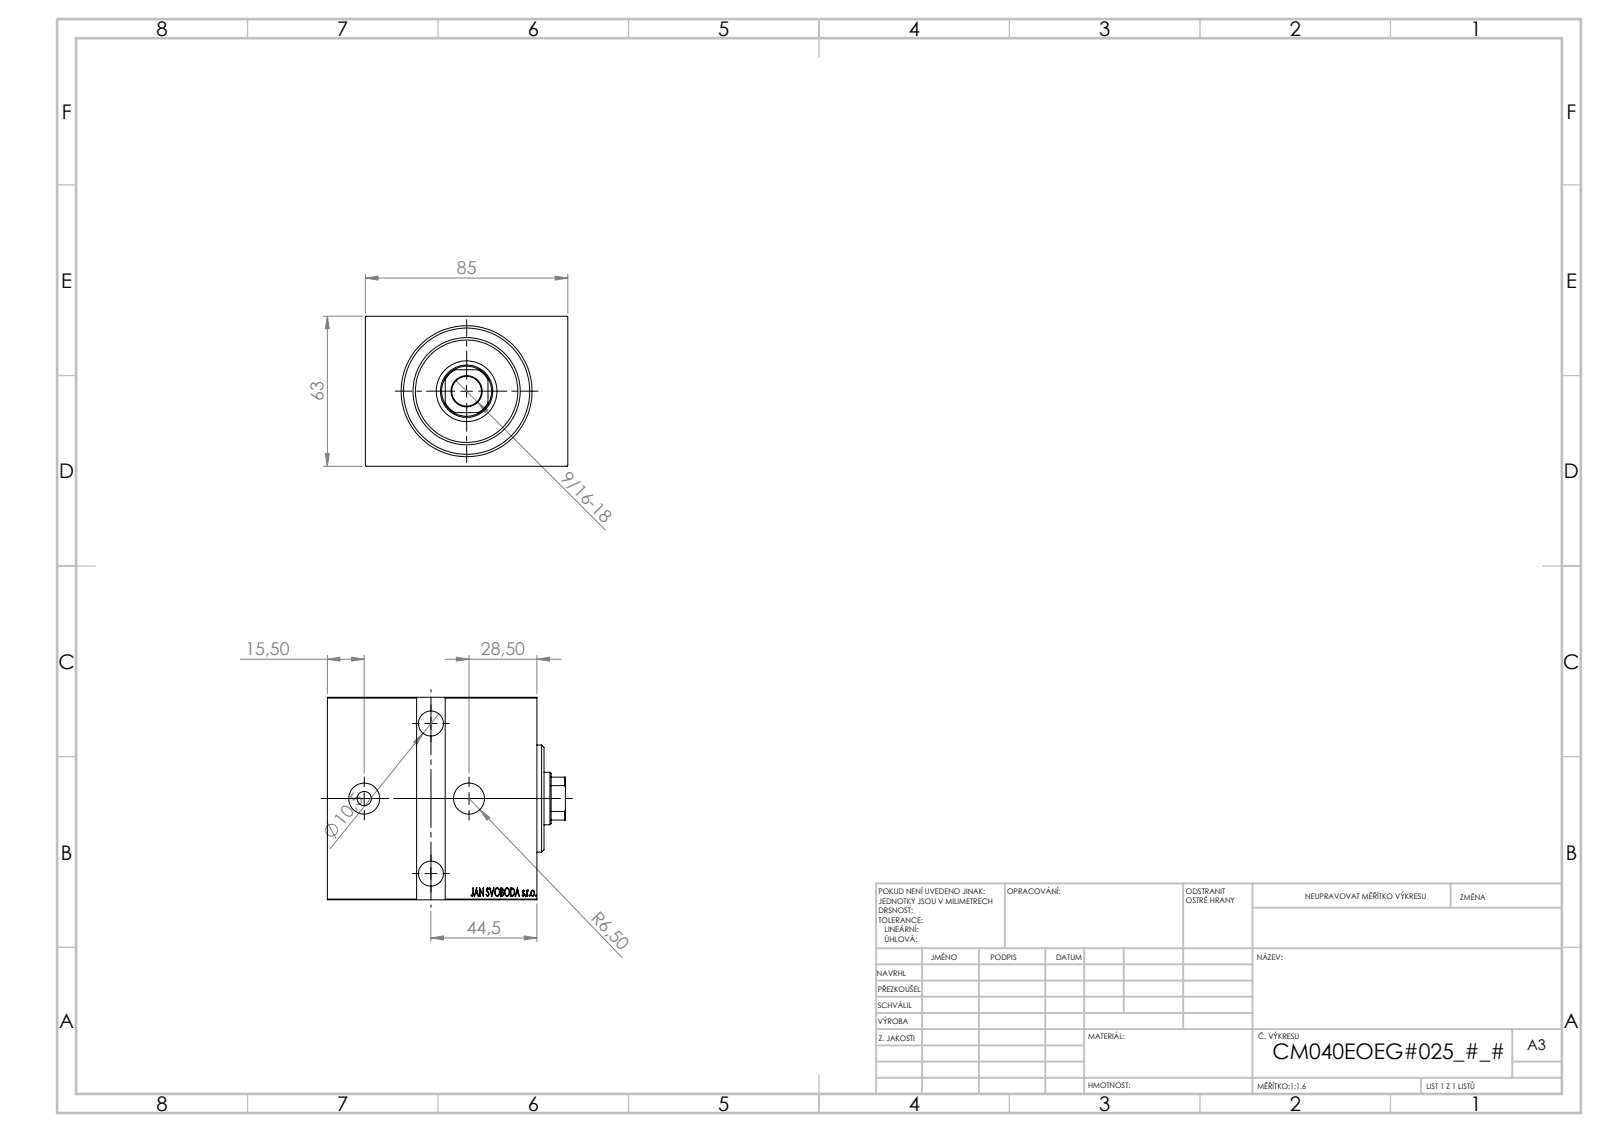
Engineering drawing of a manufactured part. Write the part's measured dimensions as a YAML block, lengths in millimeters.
part_name: "V450CM_E_VCP; V450CM_E_Body; V450CM_VC_B"
step_written_by: "SolidWorks 2019 (CONFIG_CONTROL_DESIGN)"
units: millimeters
bodies: {solids: 3, faces: 839, planar: 407, cylindrical: 38, other: 394}
overall_size: [100, 85, 63]
volume: 441689
surface_area: 70524
round_holes:
  - {diameter: 10.5, count: 2}
  - {diameter: 13, count: 2}
  - {diameter: 16.5, count: 2}
  - {diameter: 12.5, count: 1}
  - {diameter: 22, count: 1}
  - {diameter: 25.5, count: 1}
  - {diameter: 40, count: 1}
  - {diameter: 53, count: 1}
round_bosses_or_shafts:
  - {diameter: 45, count: 1}
  - {diameter: 42, count: 1}
  - {diameter: 6, count: 1}
partial_cylinders:
  - {radius: 10.5, count: 1}
face_to_face_distances: [63, 85, 88, 12, 76, 3, 5, 83, 71, 40]
hole_center_spacings: [35.33, 42.15, 44, 63]
